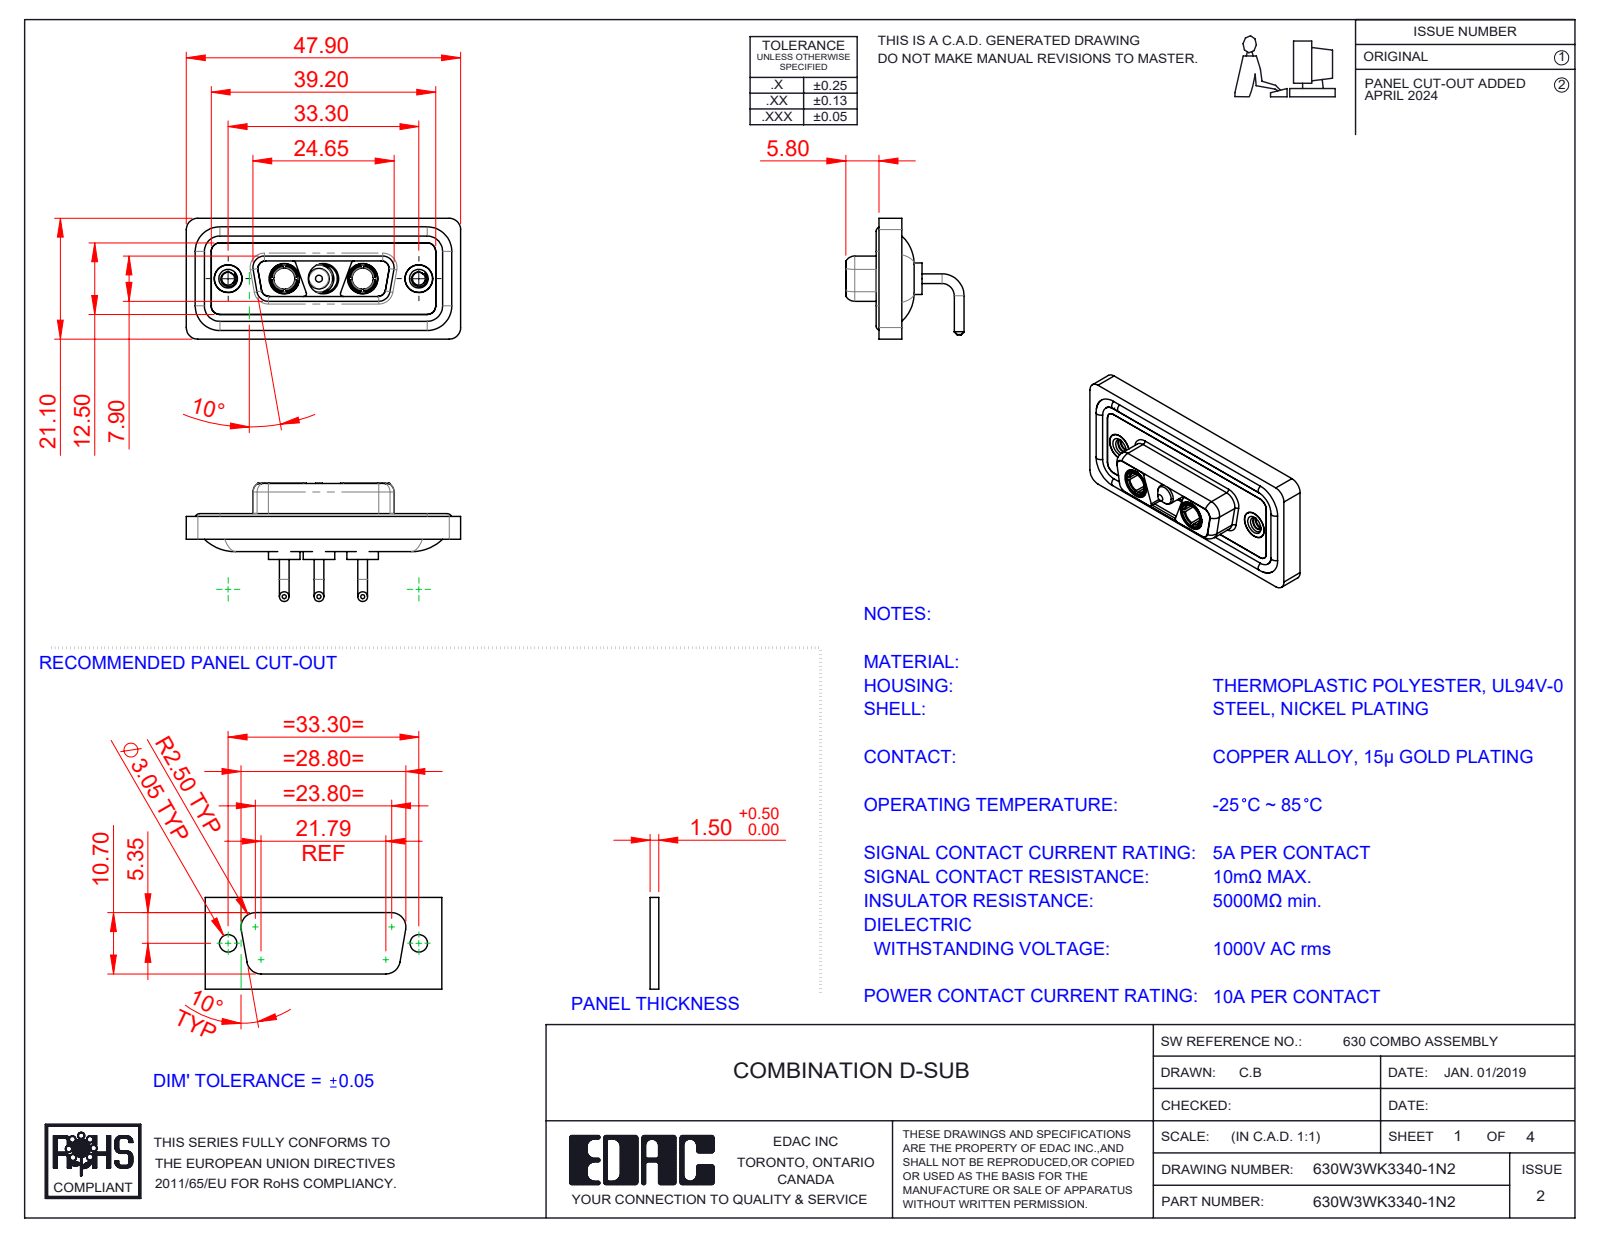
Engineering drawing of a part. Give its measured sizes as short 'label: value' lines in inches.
name: 630Combo Shell Front_15 Contacts; Power Socket_10A RA; 630Combo Threaded Rivet_2; 630Combo Housing_3WK3 (+4 more)
written by: SolidWorks 2023 (CONFIG_CONTROL_DESIGN)
unit: in
bodies: 13 solids, 595 faces (178 planar, 264 cylindrical, 153 other)
size: 1.886 × 0.831 × 0.813
volume: 0.357 in³; area: 14.86 in²
holes: 5× ⌀0.191, 3× ⌀0.209, 2× ⌀0.089, 2× ⌀0.146, 2× ⌀0.157, 2× ⌀0.159, 2× ⌀0.197
bosses: 6× ⌀0.067, 4× ⌀0.063, 3× ⌀0.217, 3× ⌀0.205, 3× ⌀0.187, 3× ⌀0.148, 2× ⌀0.195, 2× ⌀0.195
rounds: 20× R0.079, 18× R0.059, 12× R0.053, 8× R0.02, 8× R0.063, 4× R0.01, 4× R0.024, 4× R0.026
face distances: 0.016, 0.071, 0.043, 0.063, 0.114, 0.098, 0.122, 0.146, 0.059, 0.161
hole spacings: 0.27, 0.386, 0.656, 0.925, 0.539, 1.311
